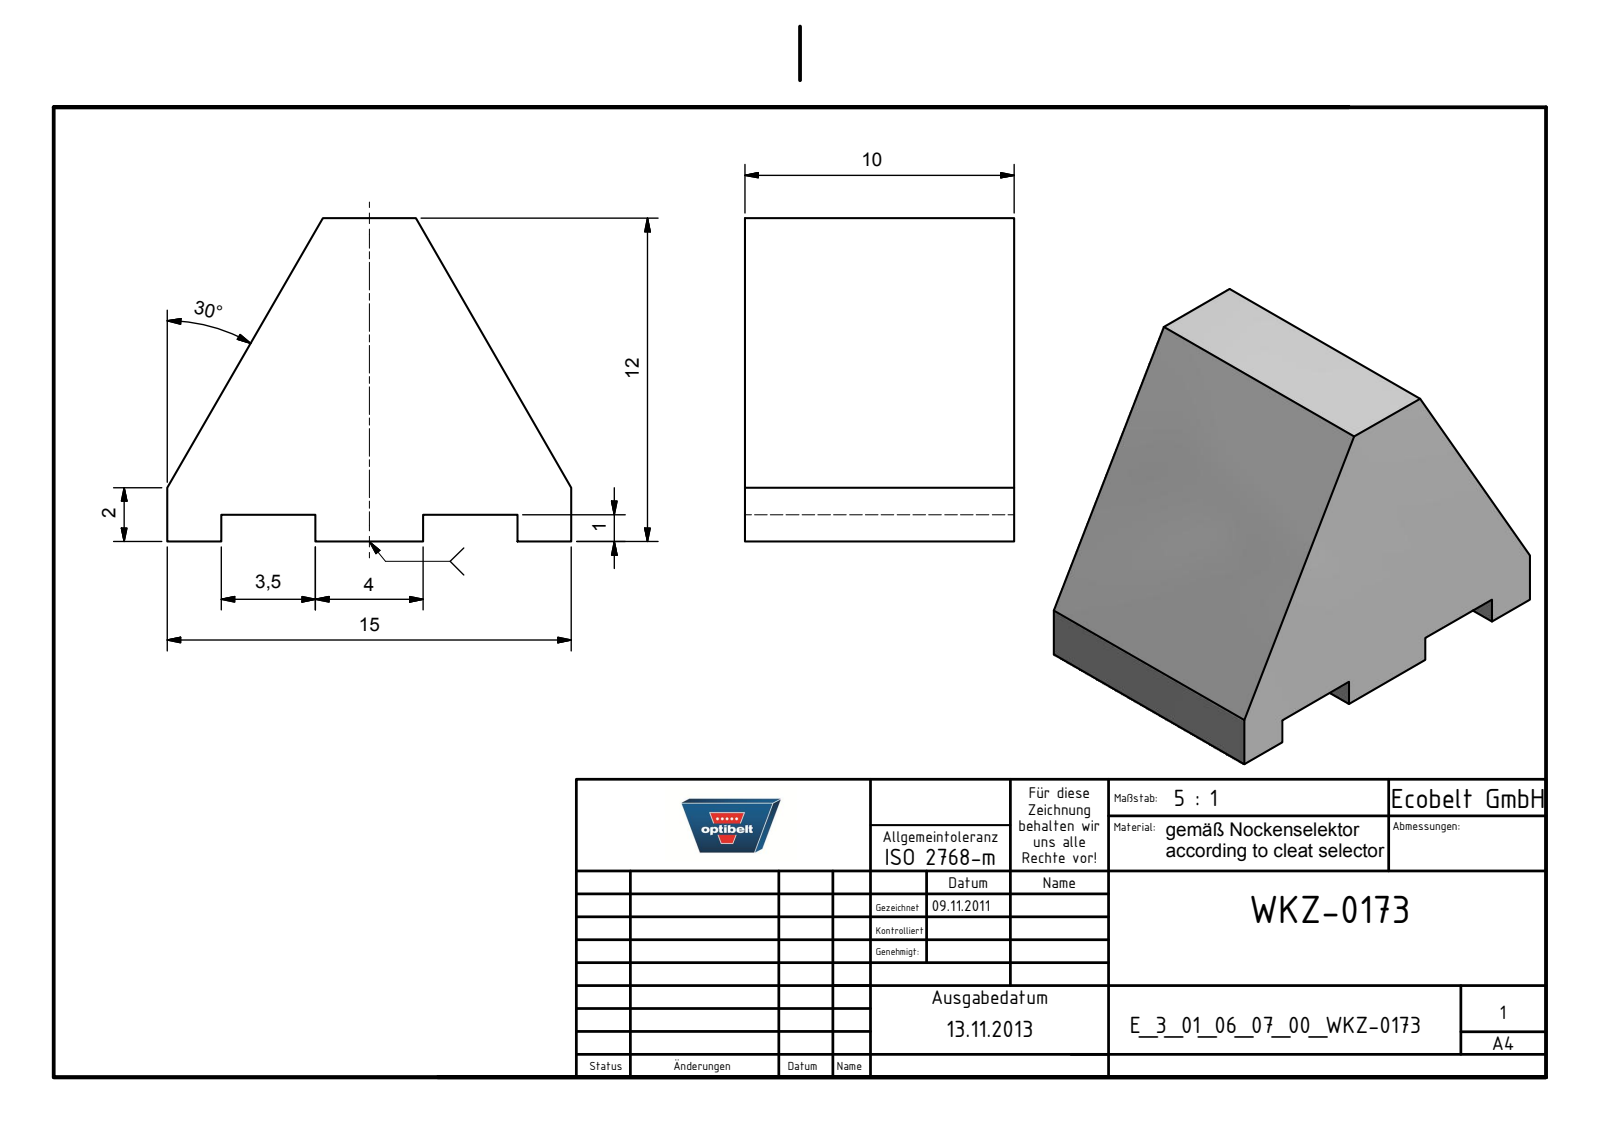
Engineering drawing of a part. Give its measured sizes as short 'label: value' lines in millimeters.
name: E_3_01_06_07_00_WKZ-0173
written by: Autodesk Inventor 2025 (AUTOMOTIVE_DESIGN)
unit: mm
bodies: 1 solid, 16 faces (16 planar, 0 cylindrical, 0 other)
size: 15 × 12 × 10
volume: 1 153 mm³; area: 726 mm²
face distances: 10, 1, 11, 12, 2, 5.5, 9.5, 13, 15, 3.5
